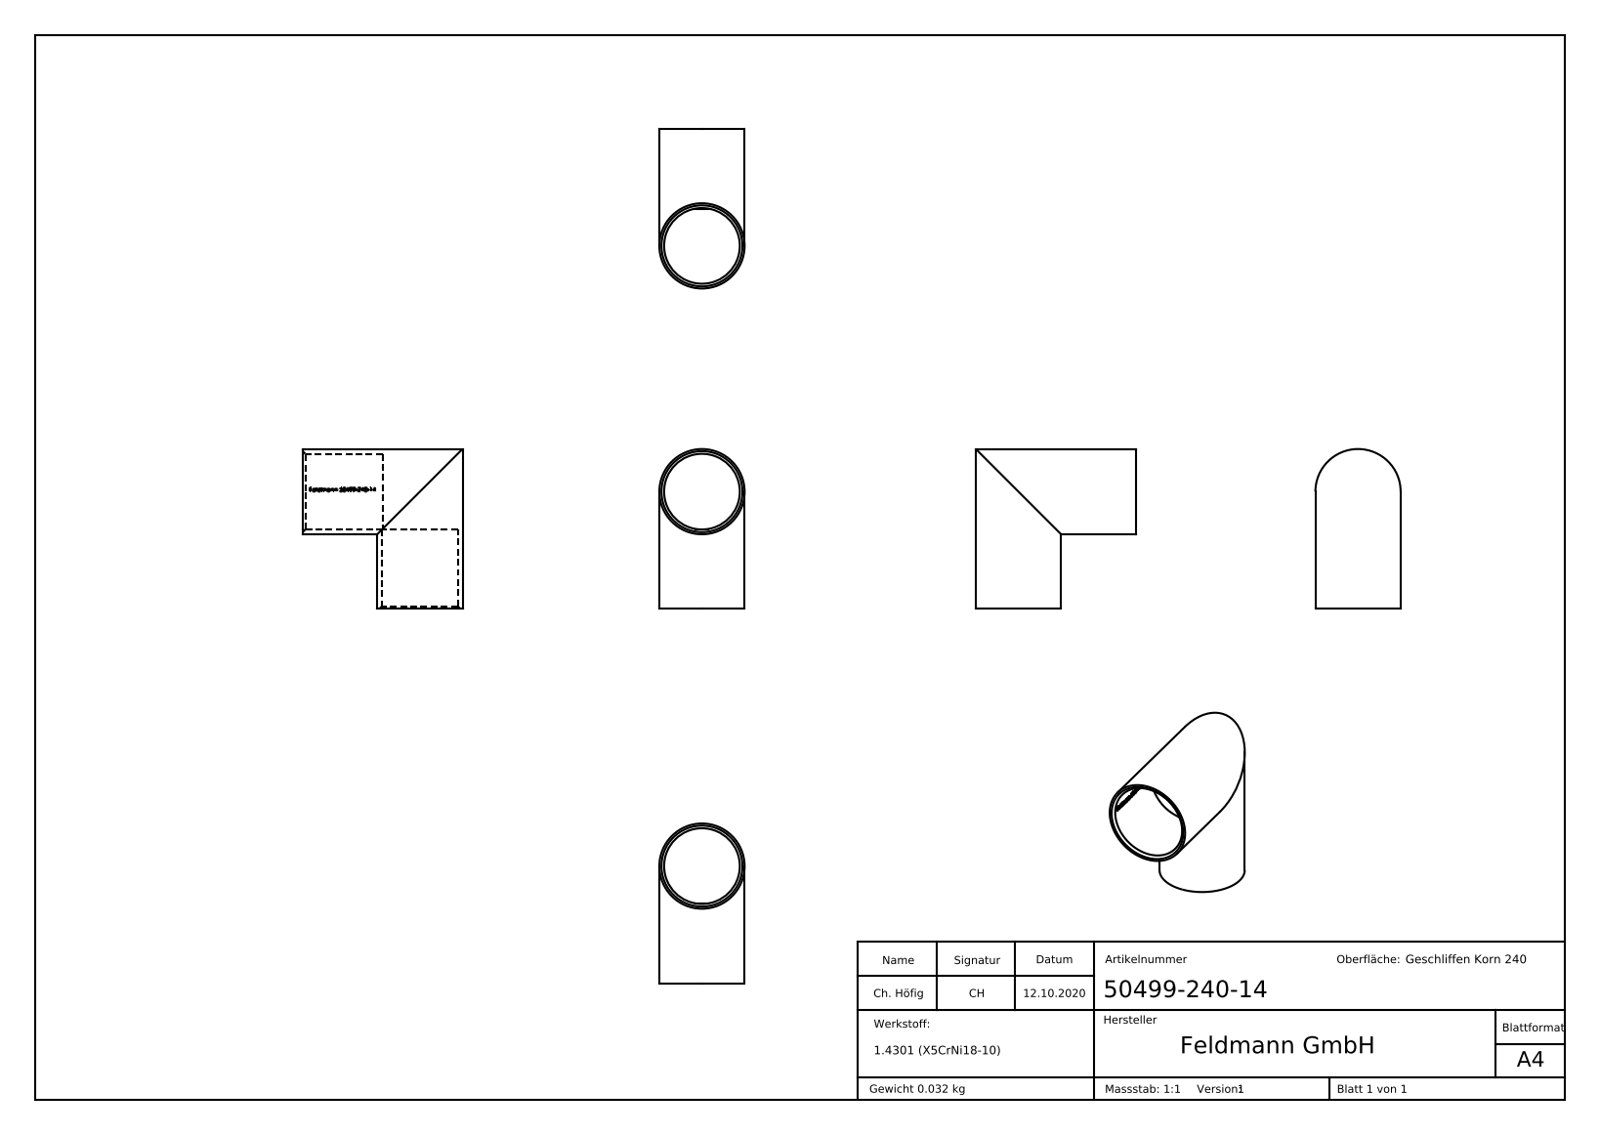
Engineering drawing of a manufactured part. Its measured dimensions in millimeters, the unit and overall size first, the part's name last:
Units: millimetres
Overall size (bounding box): 30 × 30 × 16
Round holes (diameter × count): ⌀14.2 ×2
Round bosses / shafts (diameter × count): ⌀16 ×2
Partial cylindrical surfaces — rounded edges, fillets, slot ends (radius × count): R7.2 ×1
Main face-to-face distances: 15, 2.2, 11.44, 2.13, 1.46, 9.98, 22, 7, 22.26, 7.26
Volume: 4 084 mm³ · Surface area: 3 932 mm²
Bodies: 1 solid, 269 faces (129 planar, 38 cylindrical, 102 other)
Part name (STEP PRODUCT): 50499-240-14
STEP written by: SolidWorks 2018 (CONFIG_CONTROL_DESIGN)
